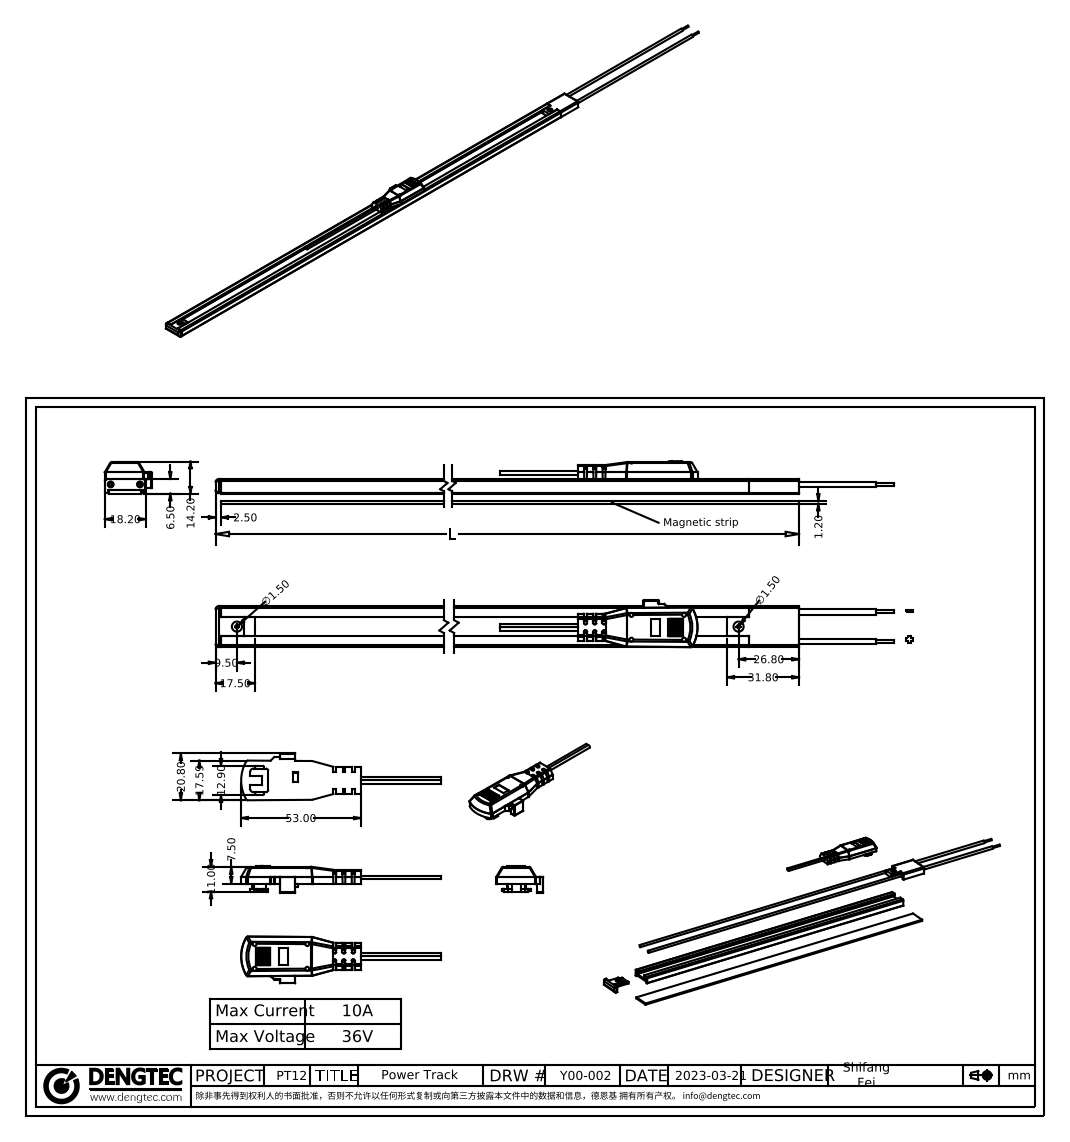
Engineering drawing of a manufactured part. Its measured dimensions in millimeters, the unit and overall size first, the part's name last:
Units: millimetres
Overall size (bounding box): 383 × 20.8 × 13.9
Round holes (diameter × count): ⌀1.8 ×4, ⌀1.5 ×2, ⌀2 ×2, ⌀2.5 ×2, ⌀4.5 ×2
Round bosses / shafts (diameter × count): ⌀2.4 ×2, ⌀1.65 ×2, ⌀1.3 ×2
Partial cylindrical surfaces — rounded edges, fillets, slot ends (radius × count): R0.2 ×24, R1 ×21, R0.5 ×8, R1.5 ×6, R16.74 ×1, R33.73 ×1
Main face-to-face distances: 1.2, 6.2, 5, 18.2, 4.6, 4.72, 13.48, 3.4, 1.6, 1
Hole centre spacings: 11, 23.3, 25.77, 13, 29.19, 29.3, 52.28, 52.34
Volume: 30 490 mm³ · Surface area: 38 695 mm²
Bodies: 10 solids, 426 faces (245 planar, 124 cylindrical, 57 other)
Part name (STEP PRODUCT): 铜皮槽; 磁铁片; 插头; 电线 (+4 more)
STEP written by: SolidWorks 2018 (AUTOMOTIVE_DESIGN)
